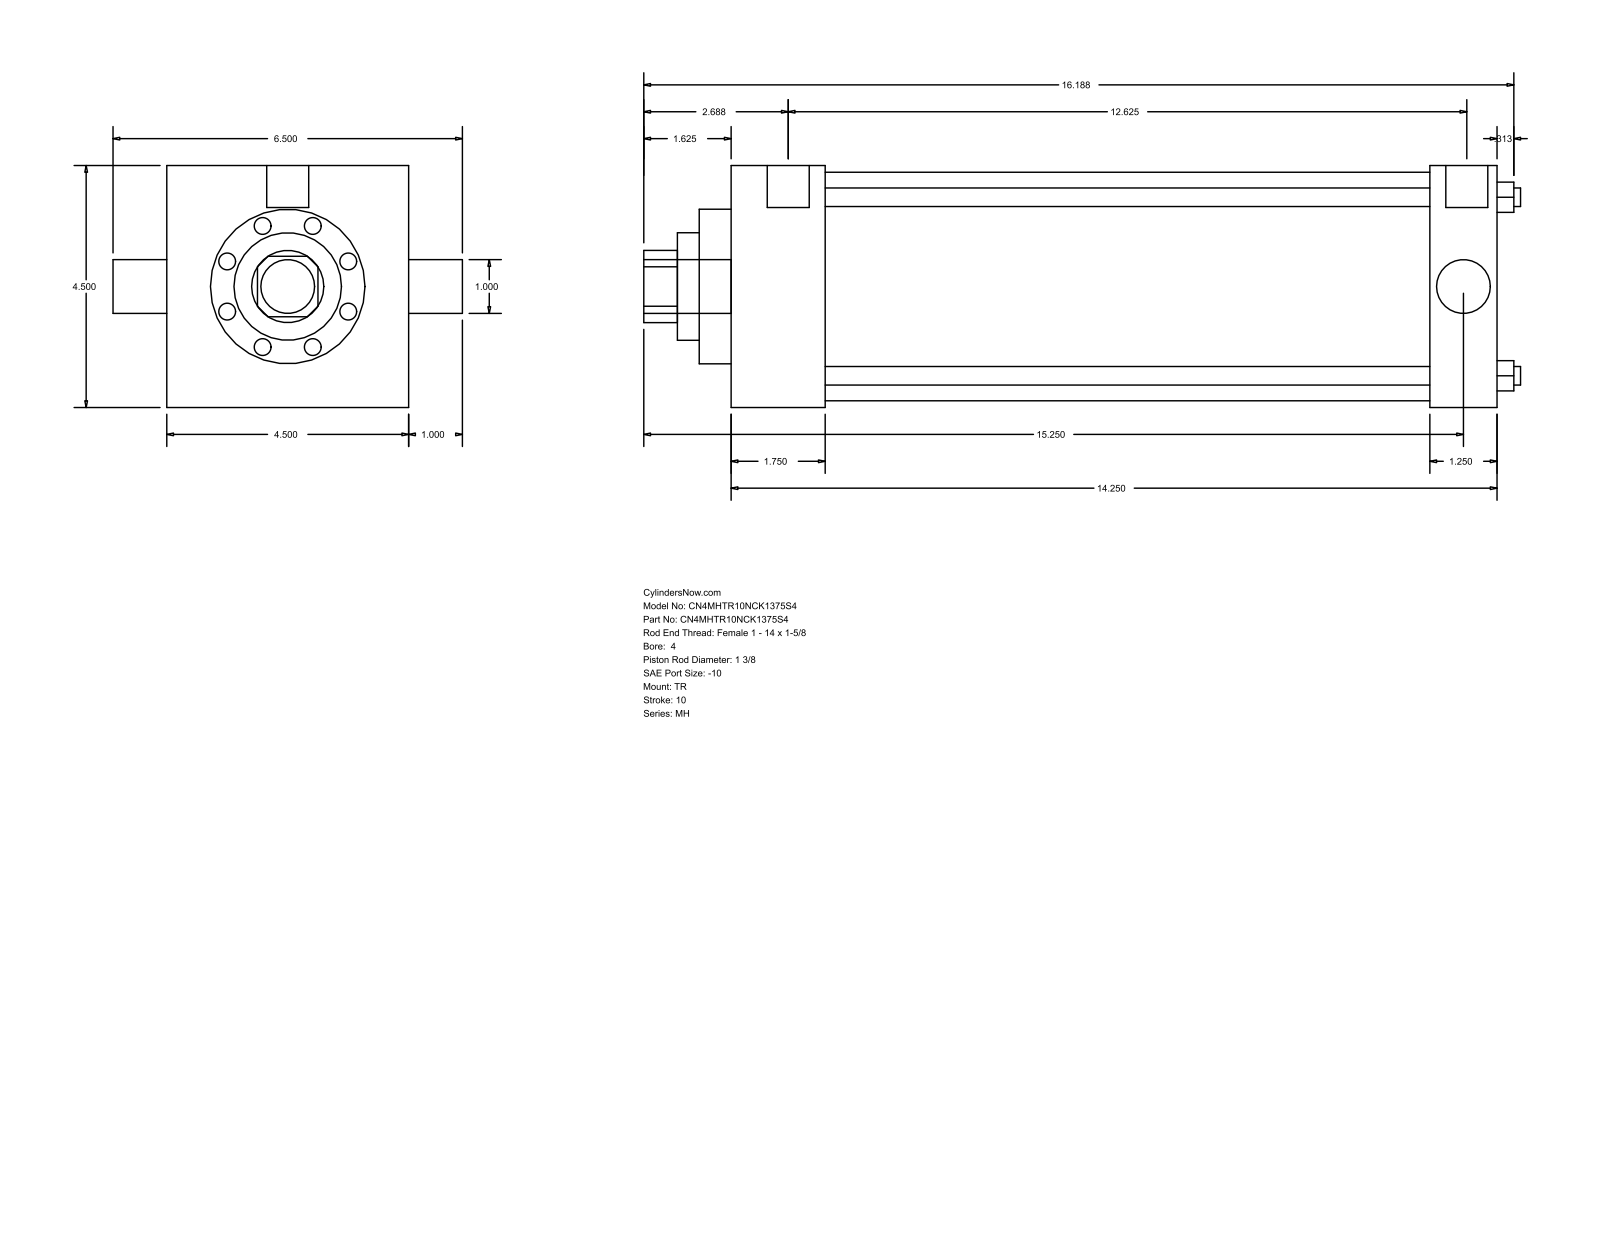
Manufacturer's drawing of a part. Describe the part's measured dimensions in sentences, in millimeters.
The part is named "MH_TR__0400_1.375". Its 3-D file was written by "GSSL Pune (CONFIG_CONTROL_DESIGN)". It is 0 solids with 86 faces: 61 planar, 25 cylindrical and 0 other. Overall it measures 414.34 by 165.1 by 114.3 millimeters. Round holes: 4 of diameter 8.76, 1 of diameter 25.4, 1 of diameter 34.92, 1 of diameter 50.8, 1 of diameter 73.03, 1 of diameter 107.95. Round bosses or shafts: 3 of diameter 8.73, 2 of diameter 19.84, 1 of diameter 25.4. Partial cylindrical surfaces (rounded edges, fillets, slot ends): 1 of radius 17.06. The main face-to-face distances are 114.3, 361.96, 44.45, 317.51, 330.21, 285.76, 31.75, 15.08, 59.53, 345.29. The hole center spacings are 59.62, 84.32, 119.25.
